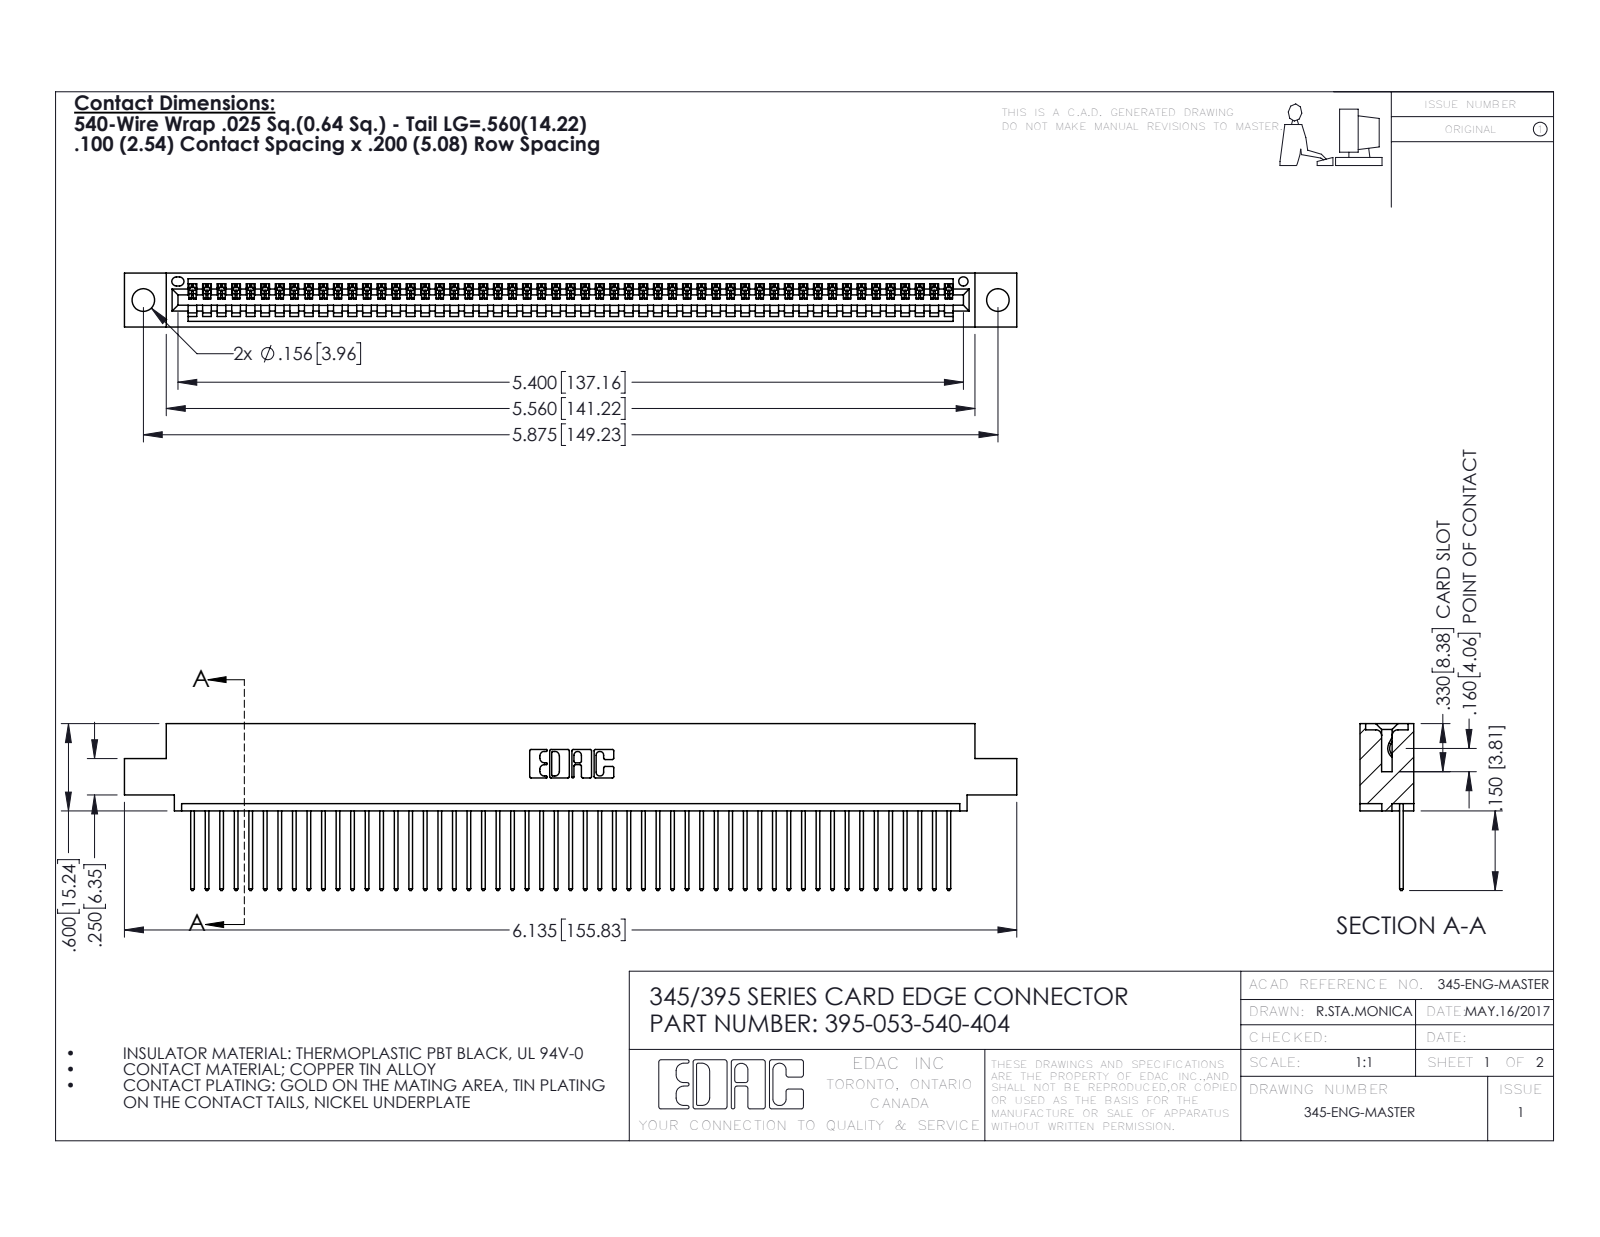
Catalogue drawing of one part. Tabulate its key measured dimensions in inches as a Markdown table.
| quantity | value |
| --- | --- |
| part name | 345 Part_0.110 Offset - 0.156 Dia-TH; 395-053-540-404; 345-292-001_345-293-140 |
| STEP written by | SolidWorks 2016 (CONFIG_CONTROL_DESIGN) |
| units | inches |
| bodies | 54 solids, 3204 faces (2204 planar, 1000 cylindrical, 0 other) |
| overall size | 6.135 × 1.147 × 0.37 |
| volume | 0.903 in³ |
| surface area | 31.35 in² |
| round holes (diameter × count) | 0.156 × 2, 0.064 × 1 |
| partial cylindrical surfaces (radius × count) | 0.006 × 106, 0.01 × 106, 0.01 × 22, 0.007 × 6, 0.031 × 6, 0.026 × 3, 0.031 × 2, 0.04 × 2 |
| main face-to-face distances | 0.298, 0.072, 0.37, 0.098, 0.272, 0.025, 0.2, 0.225, 0.149, 0.072 |
| hole center spacings | 0.27, 5.639, 5.875 |
